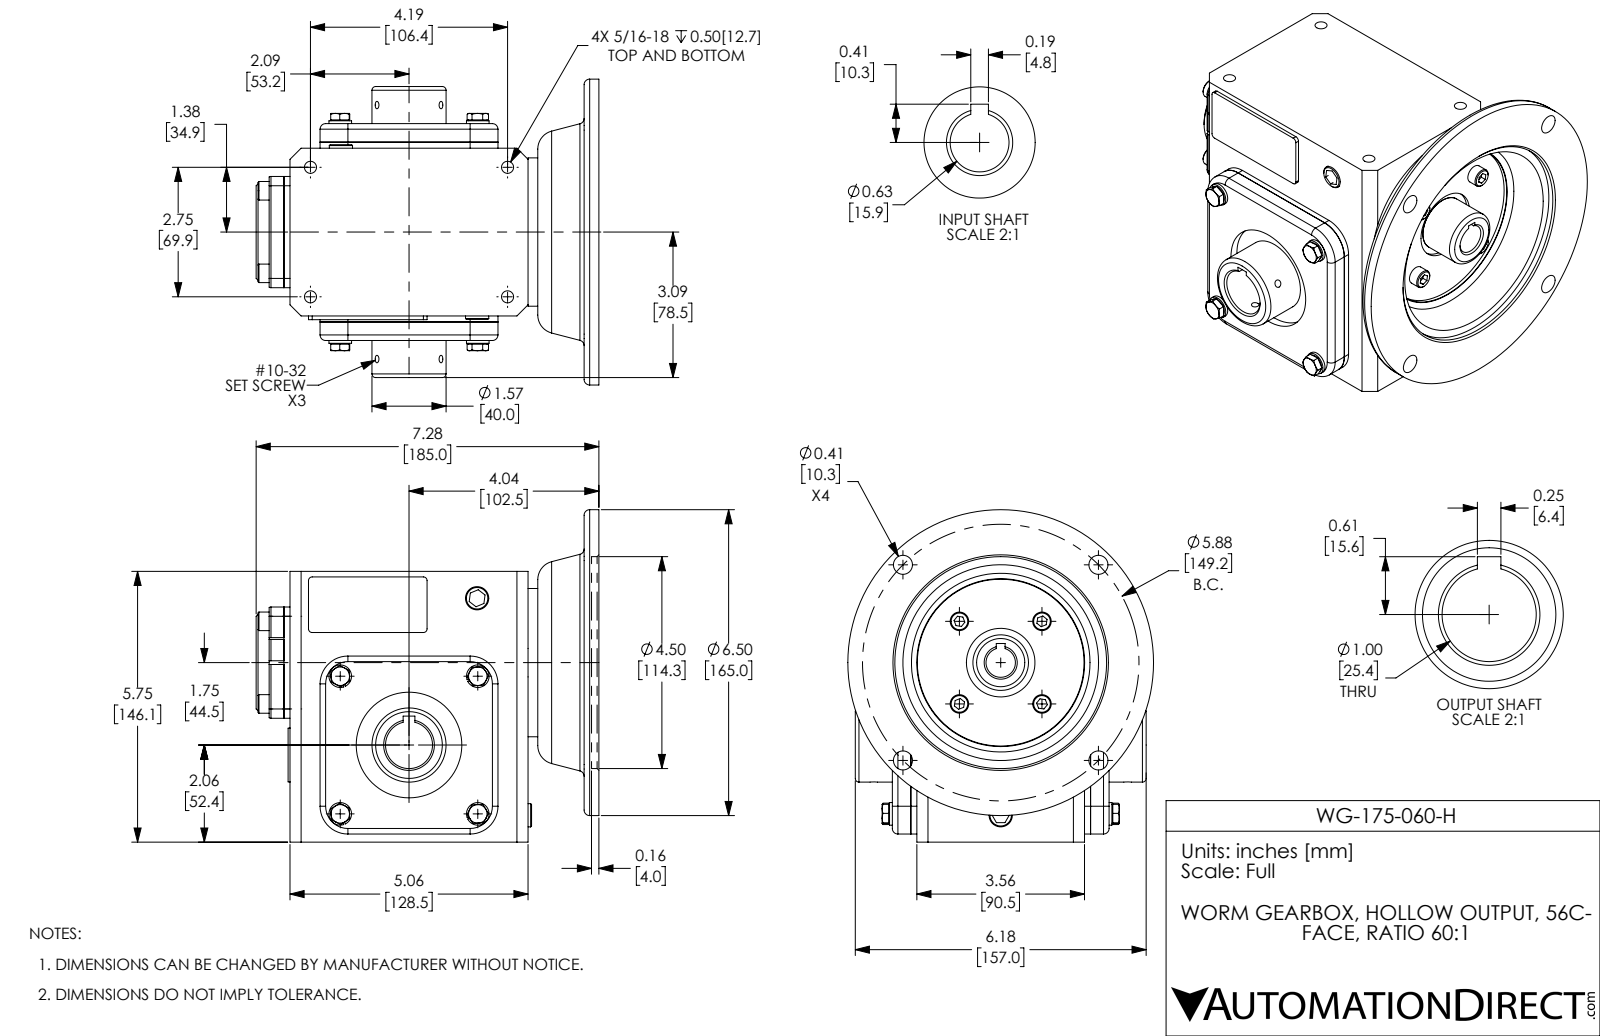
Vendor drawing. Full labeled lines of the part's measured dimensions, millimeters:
Part name (STEP PRODUCT): WG-175-060-H
STEP written by: SolidWorks 2015 (CONFIG_CONTROL_DESIGN)
Units: millimetres
Bodies: 44 solids, 661 faces (339 planar, 194 cylindrical, 128 other)
Overall size (bounding box): 185 × 179.3 × 165
Volume: 2 148 000 mm³ · Surface area: 246 900 mm²
Round holes (diameter × count): ⌀4 ×6, ⌀6.5 ×4, ⌀10.3 ×4, ⌀15 ×1, ⌀15.9 ×1, ⌀25.4 ×1, ⌀37 ×1, ⌀40 ×1, ⌀57 ×1, ⌀90 ×1, ⌀114.3 ×1
Round bosses / shafts (diameter × count): ⌀10 ×8, ⌀3 ×5, ⌀12.2 ×4, ⌀165 ×1, ⌀80 ×1, ⌀52 ×1, ⌀40 ×1, ⌀30 ×1
Partial cylindrical surfaces — rounded edges, fillets, slot ends (radius × count): R2 ×8, R3 ×8, R5 ×4, R15 ×4, R0.5 ×2, R1 ×2
Main face-to-face distances: 3.3, 97, 93.8, 10, 13.3, 103.8, 107, 146.1, 8, 170
Hole centre spacings: 62.9, 74.6, 105.5, 116.3, 137, 52.8, 69.9, 106.4
